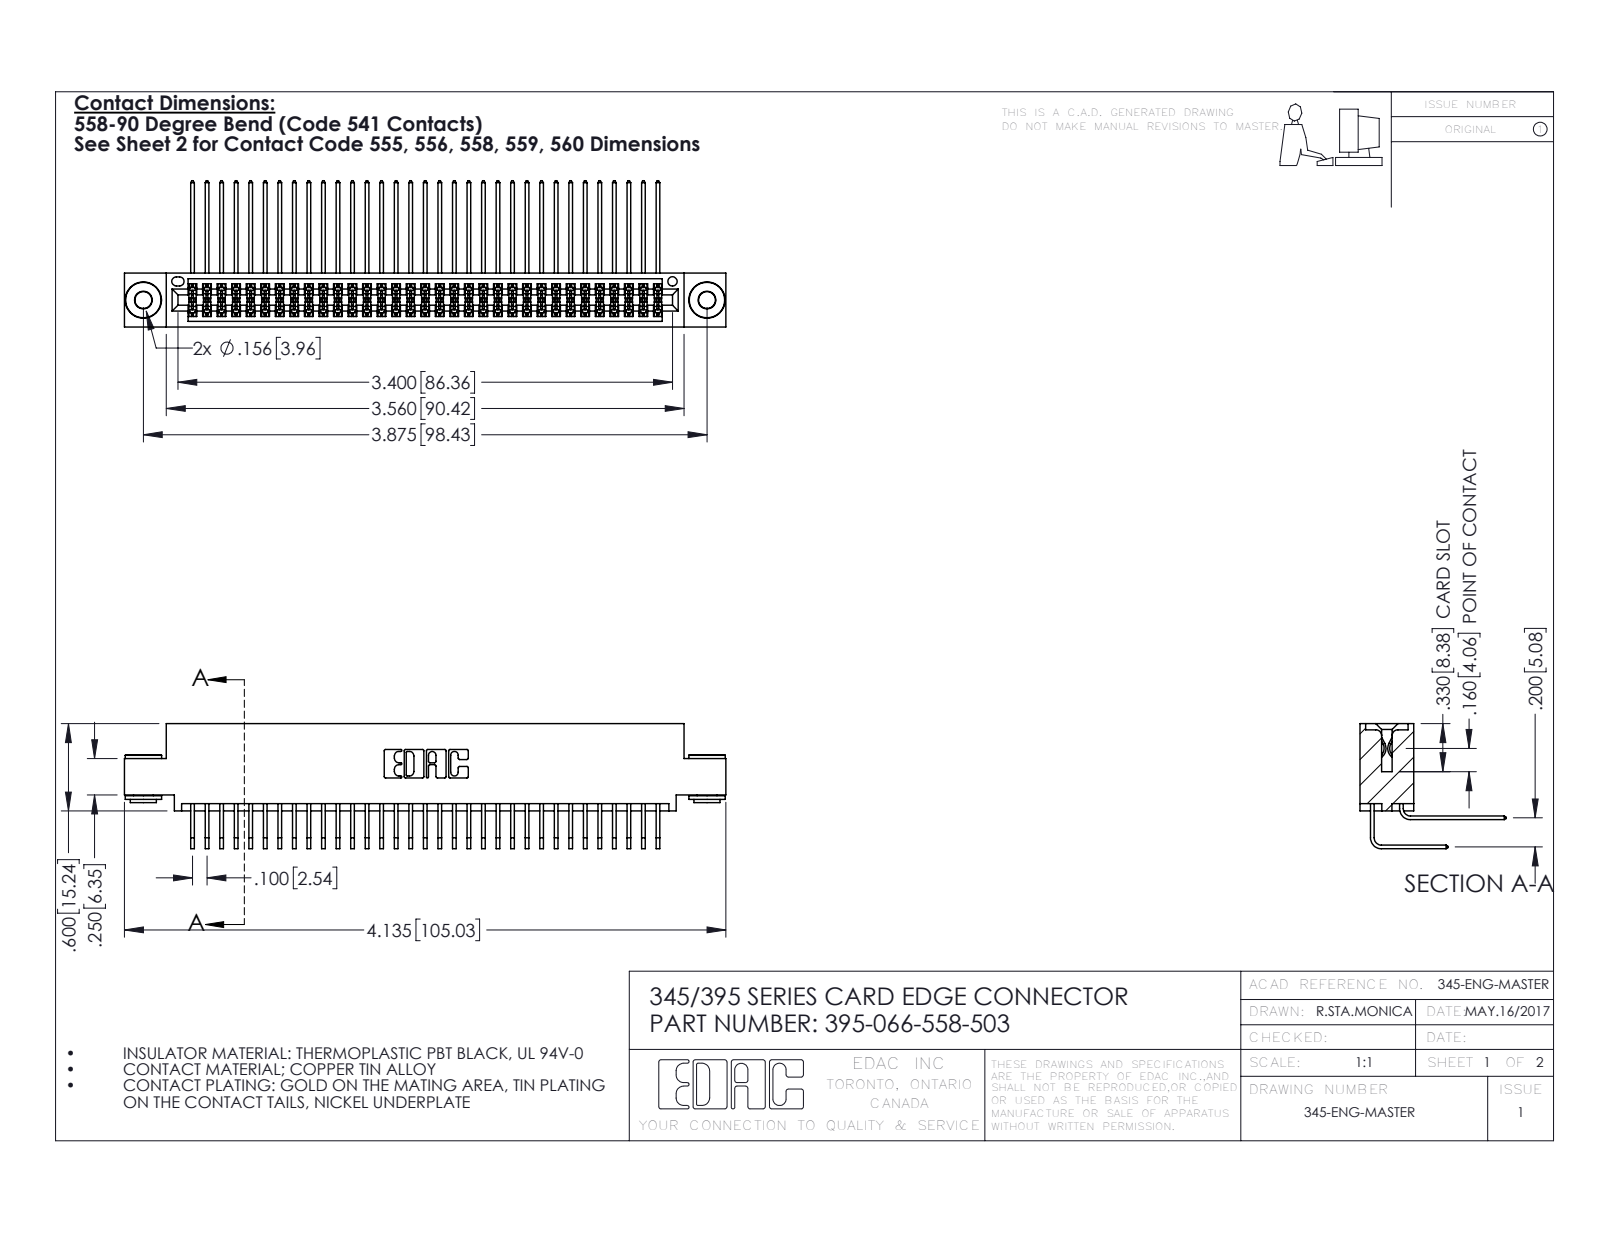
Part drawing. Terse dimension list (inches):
name: 345-292-001_558 559 Tail - 1; 395-066-558-503; 345-292-001_558 Tail - 2; 345-250-002_345-250-002-102 (+1 more)
written by: SolidWorks 2016 (CONFIG_CONTROL_DESIGN)
unit: in
bodies: 69 solids, 3600 faces (2404 planar, 1188 cylindrical, 8 other)
size: 4.135 × 1.005 × 0.859
volume: 0.637 in³; area: 26.9 in²
holes: 2× ⌀0.116, 2× ⌀0.156, 1× ⌀0.064
bosses: 2× ⌀0.25, 2× ⌀0.18, 2× ⌀0.136
rounds: 100× R0.006, 22× R0.01, 6× R0.007, 6× R0.031, 3× R0.026, 2× R0.014, 2× R0.019, 2× R0.022
face distances: 0.072, 0.298, 0.2, 0.37, 0.025, 0.098, 0.272, 0.225, 0.025, 0.175
hole spacings: 0.27, 3.64, 3.875
